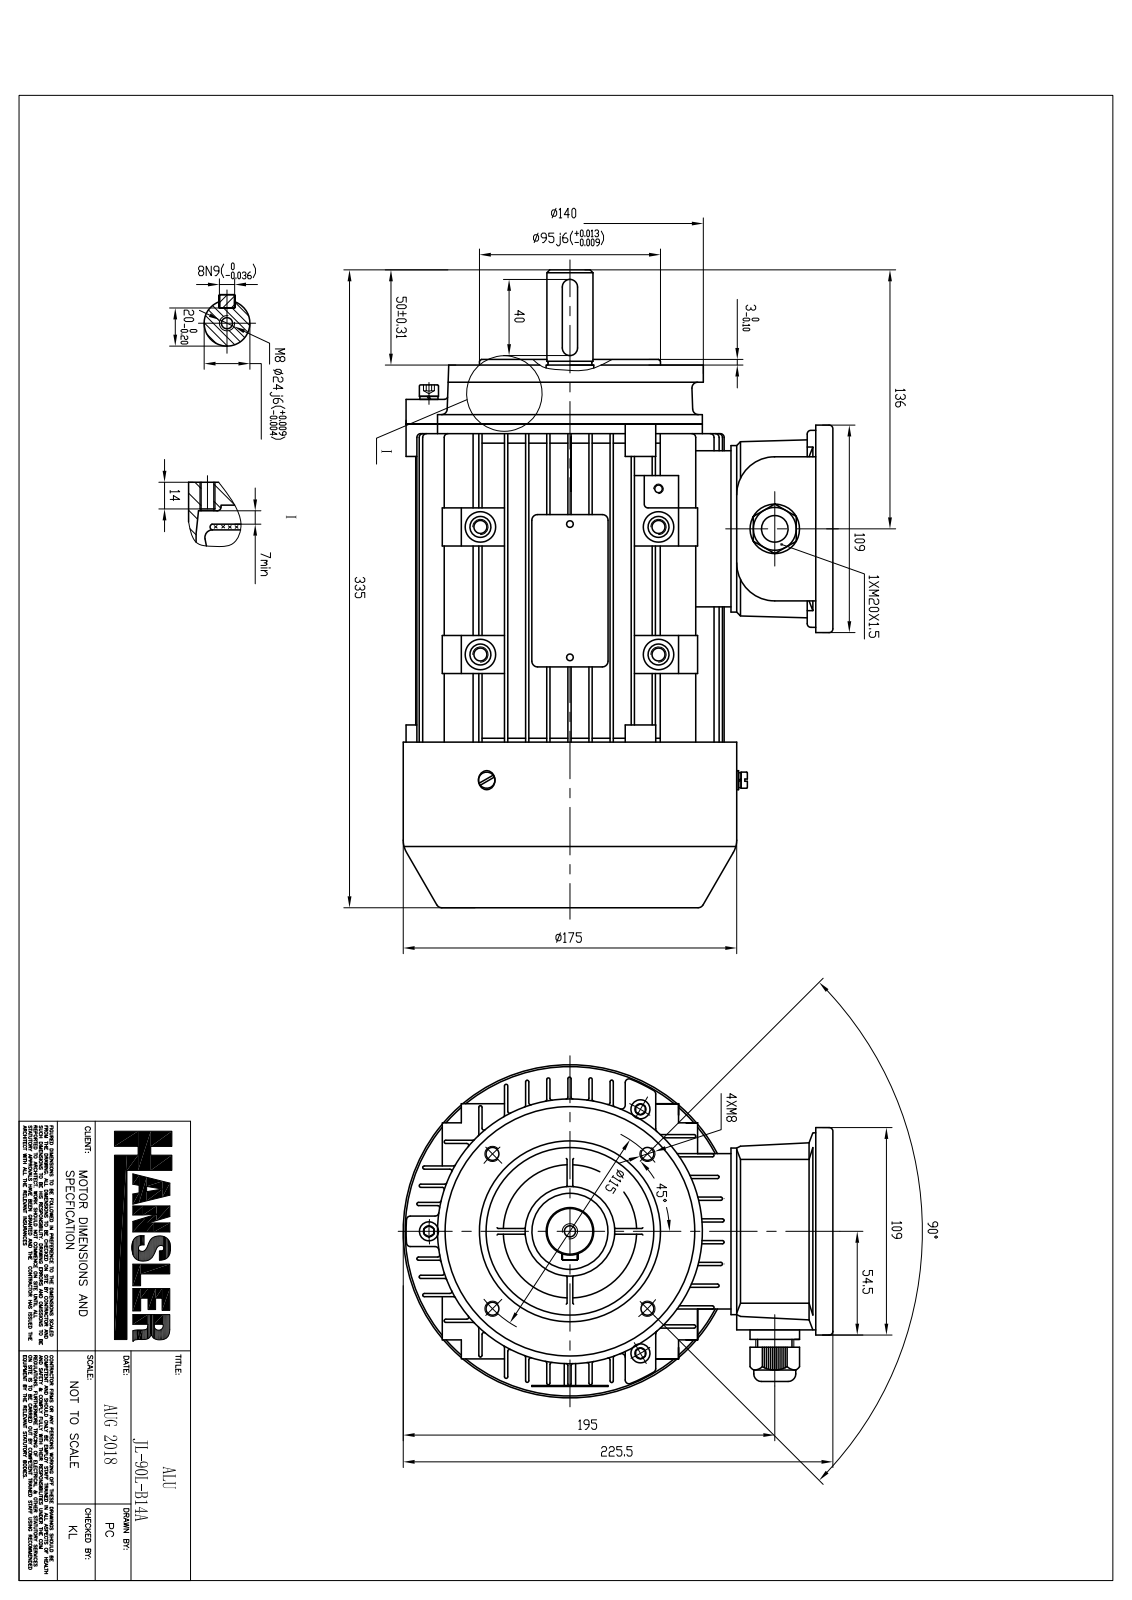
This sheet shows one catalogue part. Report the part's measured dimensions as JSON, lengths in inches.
{"part_name": "JL-90L-B14A", "step_written_by": "SIEMENS PLM Software NX 12.0 (AP203_CONFIGURATION_CONTROLLED_3D_DESIGN_OF_MECHANICAL_PARTS_AND_ASSEMBLIES_MIM_LF)", "units": "inches", "bodies": {"solids": 54, "faces": 4459, "planar": 2764, "cylindrical": 1303, "other": 392}, "overall_size": [13.189, 9.075, 6.89], "volume_in3": 84.15, "surface_area_in2": 1392, "round_holes": [[0.315, 18], [0.157, 13], [0.197, 11], [0.228, 10], [0.63, 8], [0.189, 4], [0.207, 4], [0.209, 4], [0.338, 4], [0.354, 4], [0.472, 4], [0.236, 3]], "round_bosses_or_shafts": [[0.433, 8], [0.176, 8], [0.591, 4], [0.582, 4], [0.512, 4], [0.472, 4], [0.394, 4], [0.309, 4]], "partial_cylinders_radius": [[0.02, 464], [0.039, 78], [0.079, 64], [0.157, 19], [0.03, 16], [0.197, 16], [0.118, 11], [0.276, 11]], "face_to_face_distances": [0.067, 0.436, 1.745, 0.872, 0.197, 0.098, 0.369, 1.309, 0.079, 2.181], "hole_center_spacings": [1.398, 1.733, 2, 2.248, 2.264, 2.856, 3.034, 3.202]}
